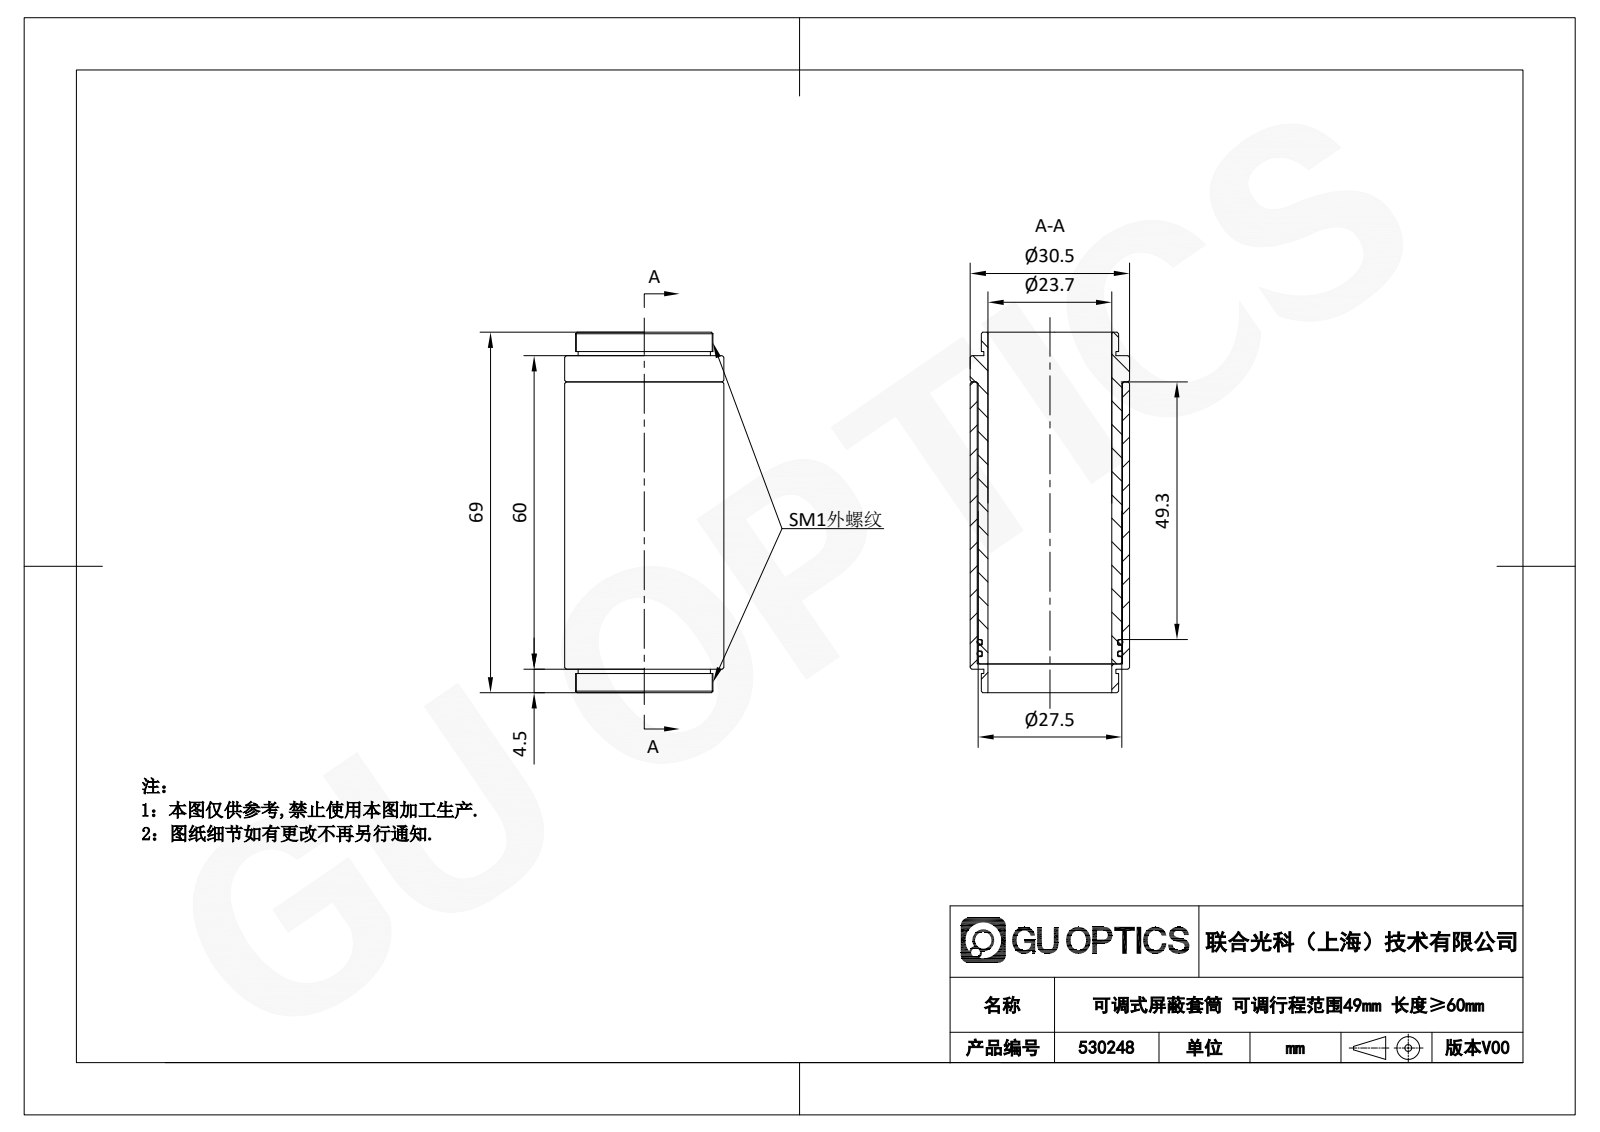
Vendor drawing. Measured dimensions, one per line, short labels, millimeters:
name: 24-26_O形圈; 3.03.31.15.208_SM1屏蔽套筒组件2_SM1-SC60-2_ZA; 3.03.31.15.209_SM1屏蔽套筒组件1_SM1-SC60-1_ZA; 530248
written by: SolidWorks 2020 (CONFIG_CONTROL_DESIGN)
unit: mm
bodies: 4 solids, 49 faces (14 planar, 14 cylindrical, 21 other)
size: 69 × 30.5 × 30.5
volume: 17 479 mm³; area: 22 938 mm²
holes: 1× ⌀23.7, 1× ⌀27.8
bosses: 1× ⌀30.5, 1× ⌀27.5, 1× ⌀26.3, 1× ⌀25.9, 1× ⌀25.3
face distances: 1, 59, 60, 5, 54, 55, 4.5, 64.5, 1.1, 2.2
